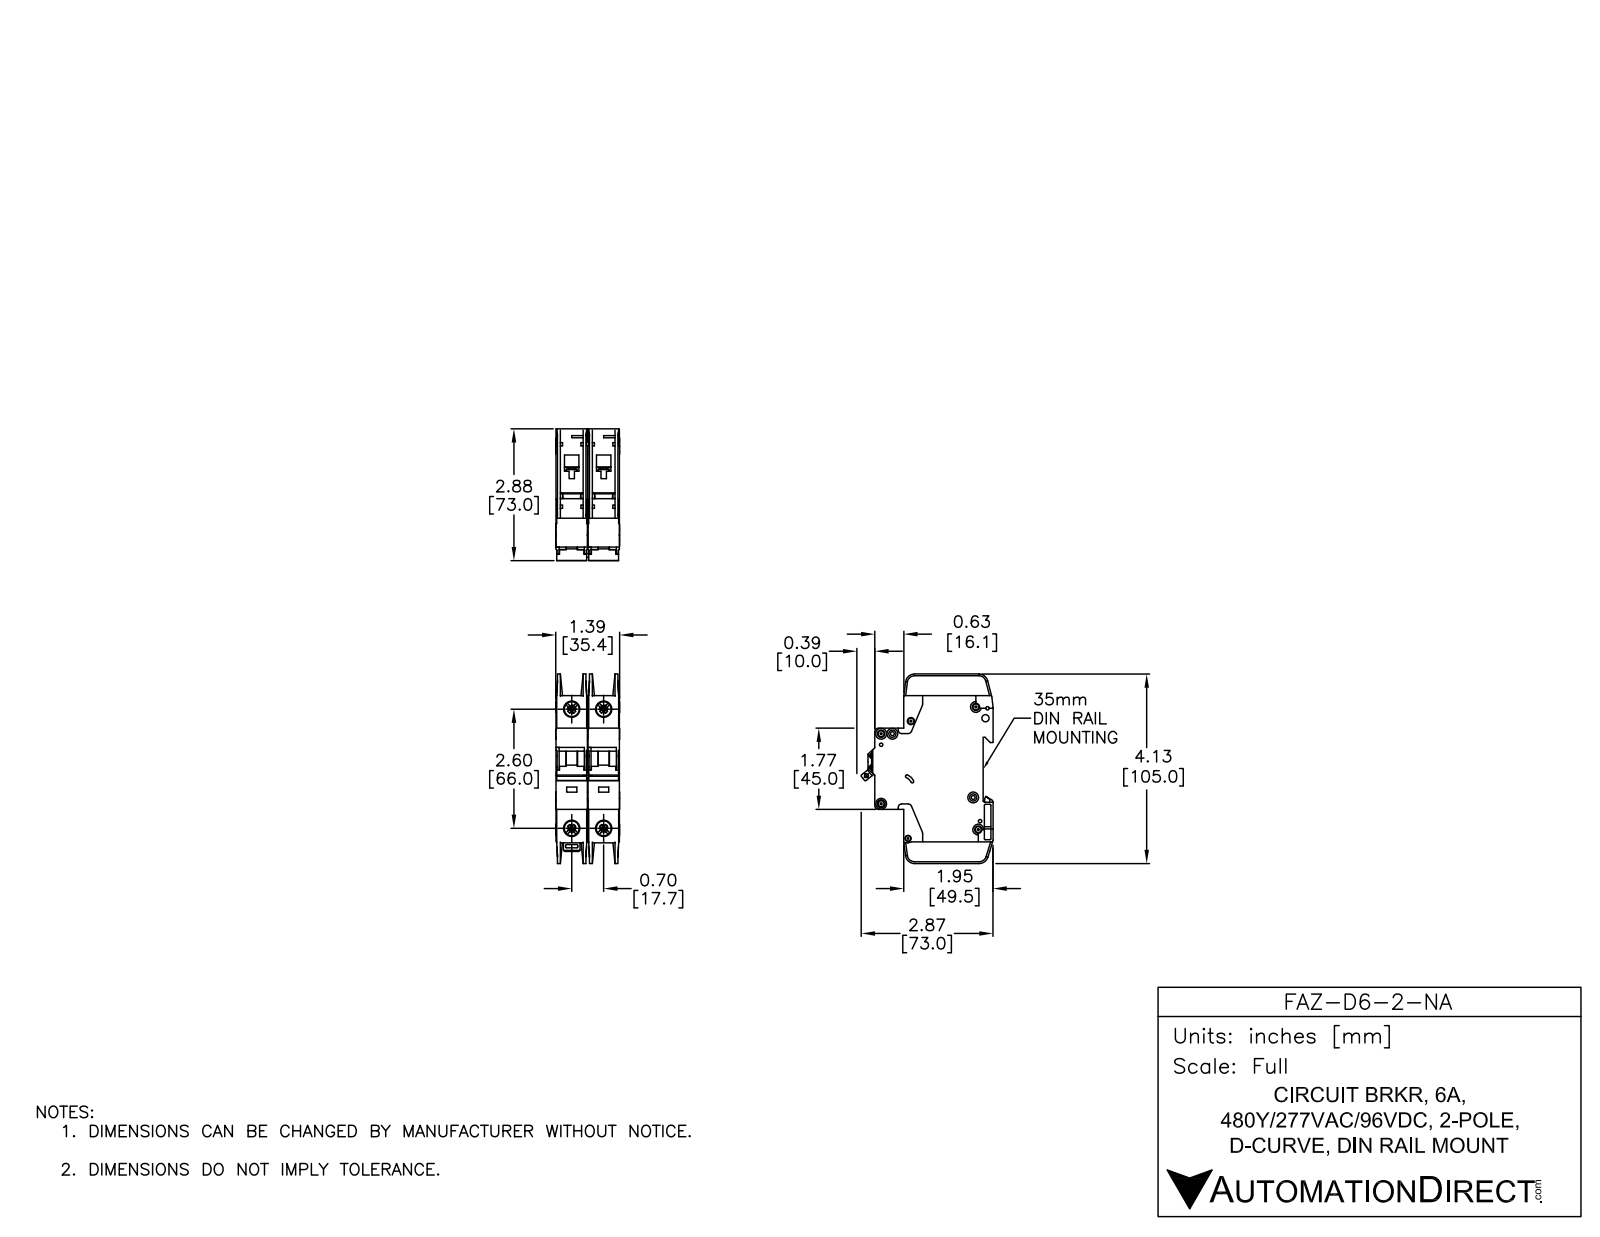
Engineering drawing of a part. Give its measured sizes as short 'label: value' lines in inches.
name: FAZ-D6-2-NA
written by: SolidWorks 2014 (AUTOMOTIVE_DESIGN)
unit: in
bodies: 6 solids, 1568 faces (818 planar, 526 cylindrical, 224 other)
size: 4.134 × 2.876 × 1.394
volume: 9.482 in³; area: 76.69 in²
holes: 7× ⌀0.142, 4× ⌀0.281, 4× ⌀0.323, 2× ⌀0.043, 2× ⌀0.059, 2× ⌀0.157, 1× ⌀0.075, 1× ⌀0.085, 1× ⌀0.087, 1× ⌀0.1, 1× ⌀0.13, 1× ⌀0.134
bosses: 7× ⌀0.236, 2× ⌀0.098
rounds: 47× R0.01, 24× R0.02, 18× R0.039, 12× R0.079, 5× R0.197, 4× R0.071, 4× R0.157, 2× R0.008
face distances: 0.697, 0.689, 0.028, 0.593, 0.096, 0.069, 0.62, 0.524, 1.386, 0.669
hole spacings: 0.244, 0.697, 2.598, 2.69, 0.204, 0.24, 0.322, 0.337
